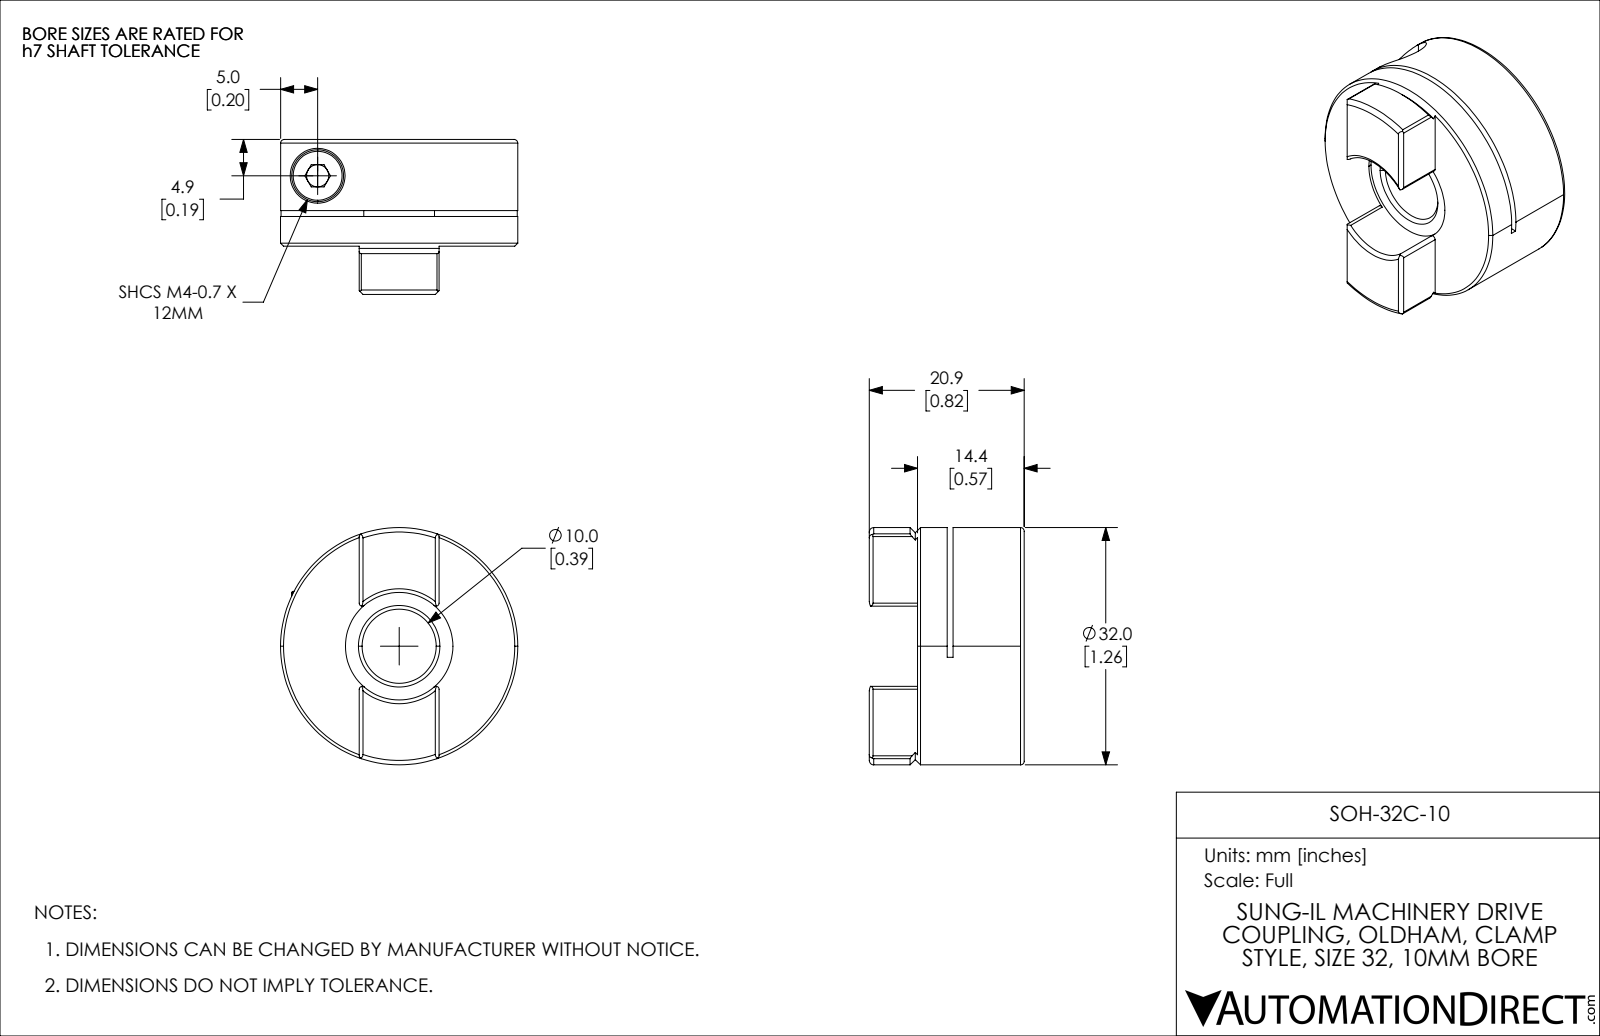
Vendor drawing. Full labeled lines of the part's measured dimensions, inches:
Part name (STEP PRODUCT): SOH-32C-10
STEP written by: SolidWorks 2021 (CONFIG_CONTROL_DESIGN)
Units: inches
Bodies: 2 solids, 97 faces (39 planar, 33 cylindrical, 25 other)
Overall size (bounding box): 1.26 × 1.26 × 0.823
Volume: 0.67 in³ · Surface area: 8.426 in²
Round holes (diameter × count): ⌀0.118 ×1, ⌀0.13 ×1, ⌀0.173 ×1, ⌀0.291 ×1, ⌀0.394 ×1, ⌀0.571 ×1
Round bosses / shafts (diameter × count): ⌀1.26 ×1, ⌀0.276 ×1, ⌀0.157 ×1
Partial cylindrical surfaces — rounded edges, fillets, slot ends (radius × count): R0.016 ×8, R0.984 ×1
Main face-to-face distances: 0.157, 0.567, 0.409, 0.378, 0.031, 0.189, 0.039, 0.823, 0.445, 0.413
